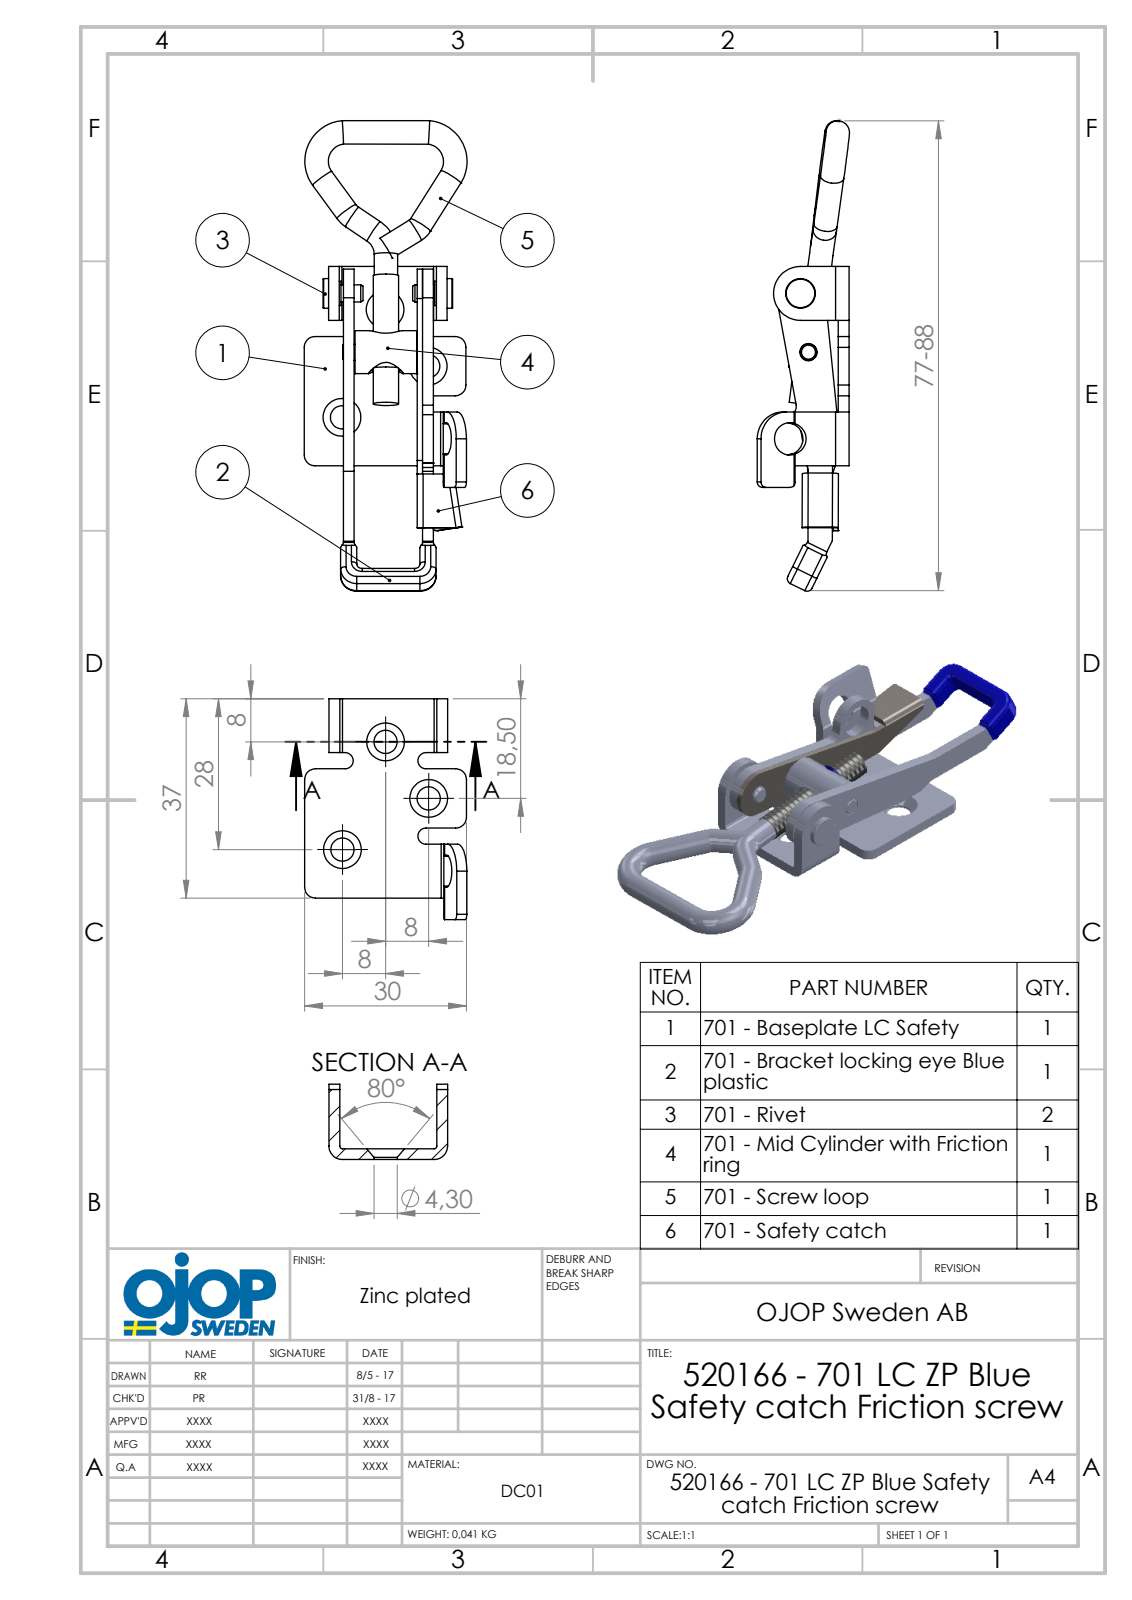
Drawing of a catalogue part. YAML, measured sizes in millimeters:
part_name: "520166 - 701 LC ZP Blue Safety catch Friction screw; 701 - Mid Cylinder with Friction ring; 701 - Säkerhetsspärr; 701 - Skruvögla (+5 more)"
step_written_by: "SolidWorks 2015 (AUTOMOTIVE_DESIGN)"
units: millimeters
bodies: {solids: 8, faces: 284, planar: 114, cylindrical: 126, other: 44}
overall_size: [87.35, 30.2, 17.11]
volume: 6820
surface_area: 8735
round_holes:
  - {diameter: 4.3, count: 4}
  - {diameter: 3.2, count: 2}
  - {diameter: 4.5, count: 1}
  - {diameter: 6, count: 1}
  - {diameter: 6.5, count: 1}
round_bosses_or_shafts:
  - {diameter: 4.36, count: 5}
  - {diameter: 8, count: 1}
  - {diameter: 5.5, count: 1}
  - {diameter: 4.7, count: 1}
  - {diameter: 3.15, count: 1}
  - {diameter: 3, count: 1}
partial_cylinders:
  - {radius: 1, count: 22}
  - {radius: 0.5, count: 5}
  - {radius: 1.5, count: 5}
  - {radius: 2, count: 4}
  - {radius: 2.5, count: 4}
  - {radius: 0.1, count: 3}
  - {radius: 1.1, count: 3}
  - {radius: 3, count: 3}
face_to_face_distances: [2, 14.7, 1, 3, 12.7, 16.7, 11.7, 13.7, 17.45, 2.55]
hole_center_spacings: [11, 13.2, 16.59, 18.61, 21.54, 27.11]
